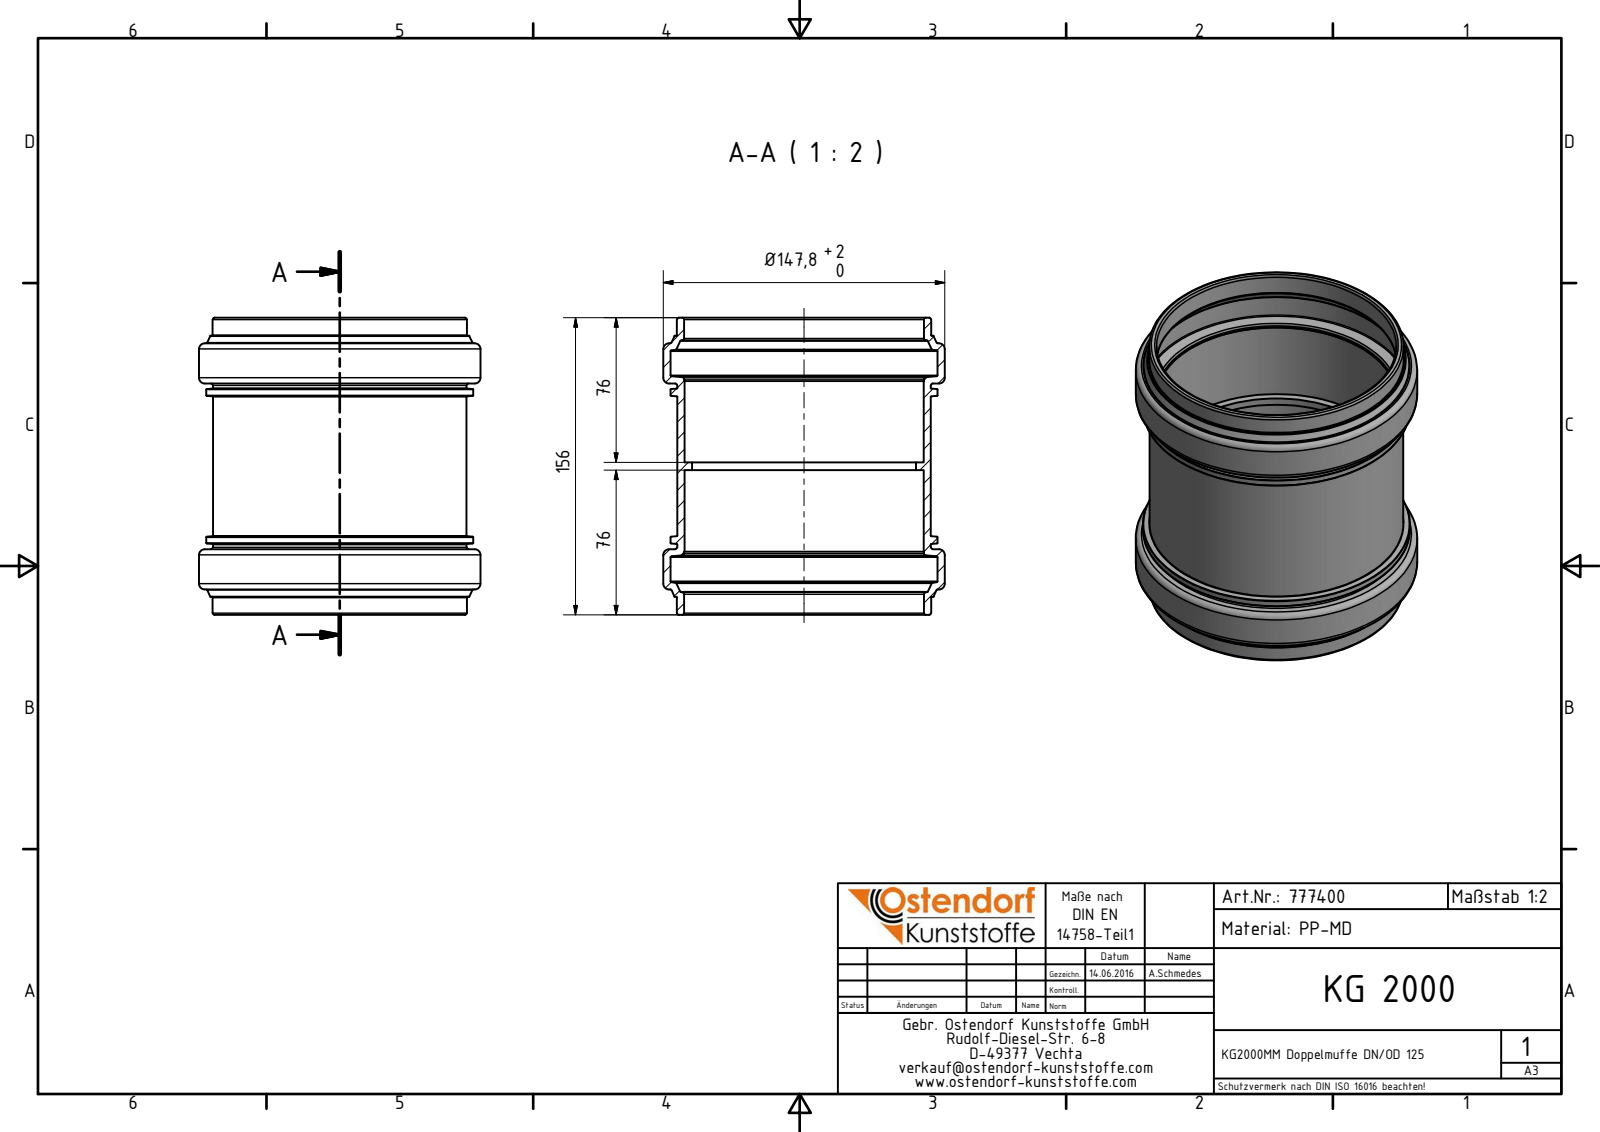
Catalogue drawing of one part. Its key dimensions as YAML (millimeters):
part_name: "777400 KG2000MM Doppelmuffe DN_OD 125"
step_written_by: "Autodesk Inventor 2016 (AUTOMOTIVE_DESIGN)"
units: millimeters
bodies: {solids: 1, faces: 80, planar: 12, cylindrical: 18, other: 50}
overall_size: [156, 147.8, 147.8]
volume: 298807
surface_area: 158348
round_holes:
  - {diameter: 117.6, count: 1}
  - {diameter: 125.6, count: 1}
  - {diameter: 125.9, count: 1}
  - {diameter: 140.2, count: 1}
round_bosses_or_shafts:
  - {diameter: 147.8, count: 1}
  - {diameter: 133.5, count: 1}
  - {diameter: 133.2, count: 1}
face_to_face_distances: [41.5, 45.5, 4, 34.5, 76, 80, 121.5, 87, 156, 13.4]
